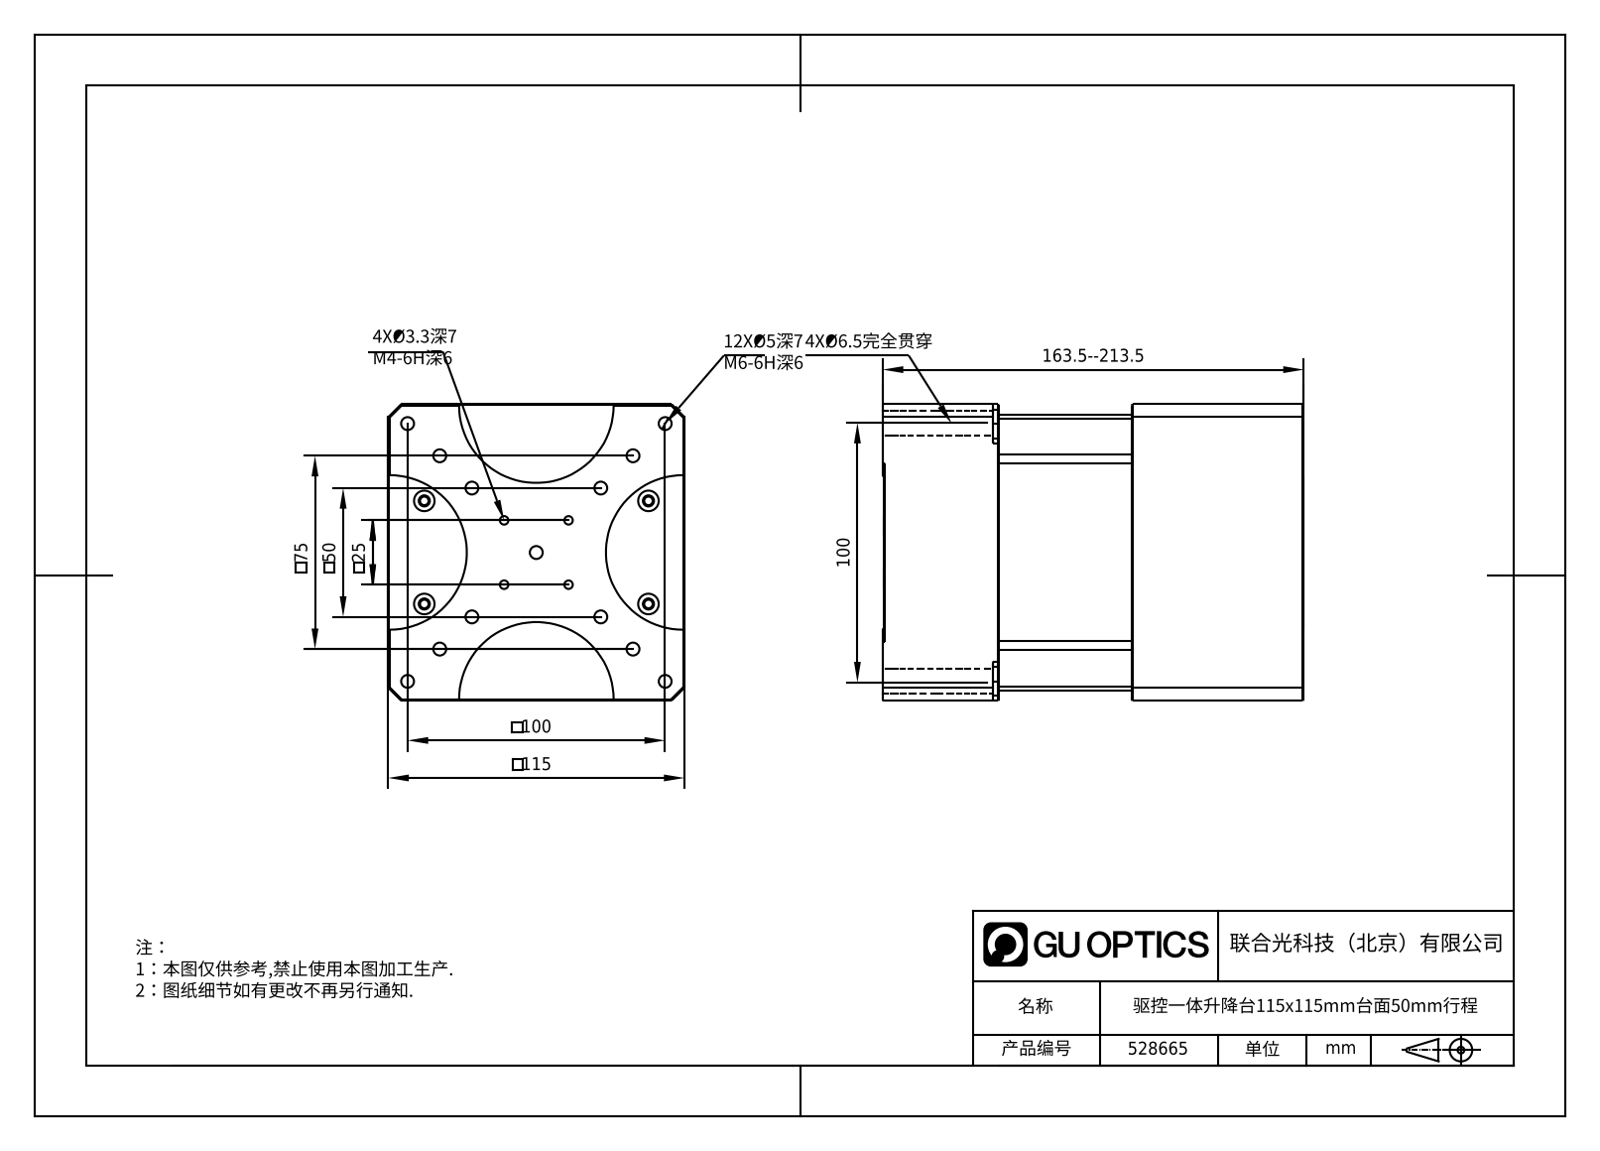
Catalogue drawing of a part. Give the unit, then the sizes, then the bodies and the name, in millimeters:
Units: millimetres
Overall size (bounding box): 163.5 × 115 × 115
Round holes (diameter × count): ⌀3.3 ×23, ⌀4.3 ×20, ⌀8 ×18, ⌀5 ×13, ⌀1.6 ×8, ⌀2.5 ×8, ⌀6.5 ×8, ⌀2.05 ×6, ⌀2.2 ×6, ⌀4 ×6, ⌀4.4 ×6, ⌀10 ×5
Round bosses / shafts (diameter × count): ⌀7 ×10, ⌀4 ×10, ⌀9.5 ×8, ⌀4.5 ×6, ⌀3.8 ×6, ⌀2.5 ×6, ⌀2 ×6, ⌀5.5 ×4
Partial cylindrical surfaces — rounded edges, fillets, slot ends (radius × count): R5 ×32, R2 ×18, R0.3 ×8, R0.5 ×4, R1 ×4, R4 ×4, R4.25 ×4, R5.75 ×4
Main face-to-face distances: 4, 107, 8, 111, 103, 7.5, 115, 87, 3, 17.5
Hole centre spacings: 88.39, 17.68, 35.36, 40, 53.03, 70.71, 22.41, 26.97
Bodies: 0 solids, 3294 faces (1710 planar, 676 cylindrical, 908 other)
Part name (STEP PRODUCT): 528665
STEP written by: SolidWorks 2020 (CONFIG_CONTROL_DESIGN)
